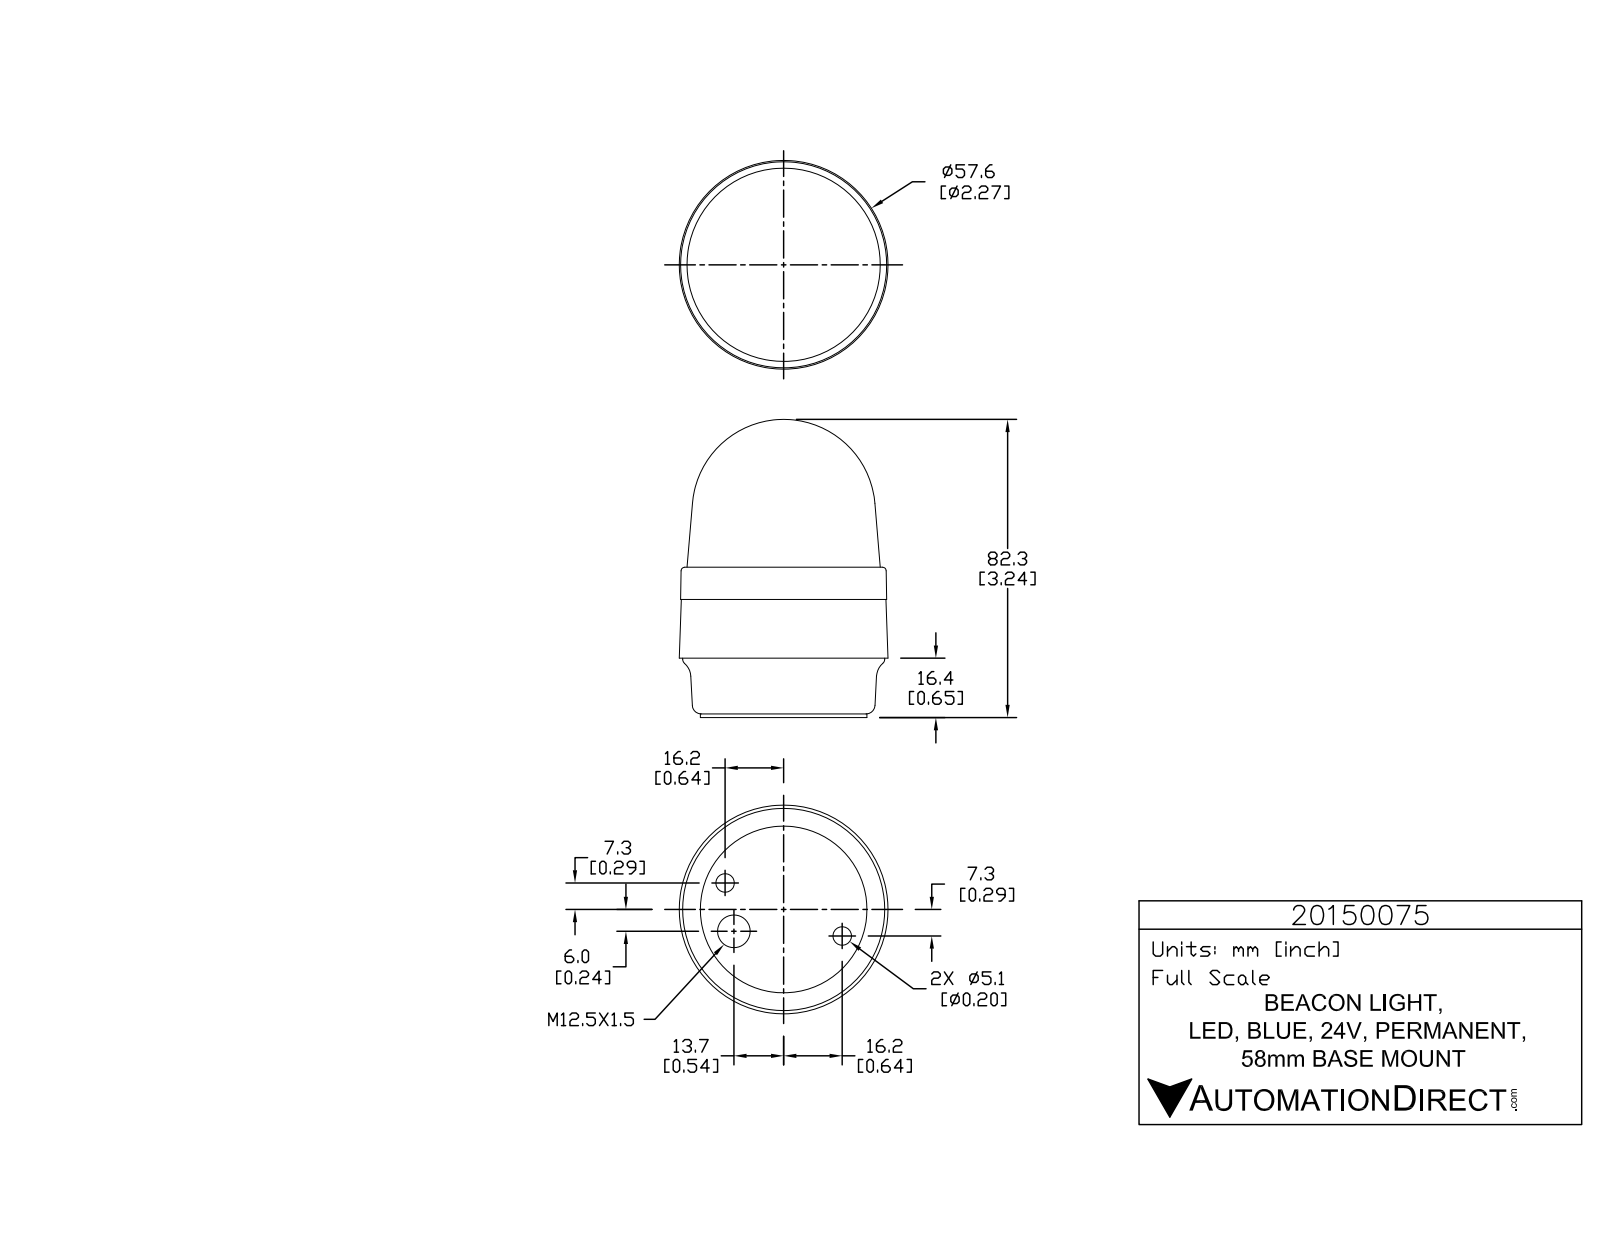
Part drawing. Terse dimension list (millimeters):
name: 20150075
written by: SolidWorks 2015 (AUTOMOTIVE_DESIGN)
unit: mm
bodies: 1 solid, 763 faces (527 planar, 145 cylindrical, 91 other)
size: 82.3 × 57.63 × 57.63
volume: 164 395 mm³; area: 16 261 mm²
holes: 3× ⌀0.99, 2× ⌀5.11, 1× ⌀9
bosses: 3× ⌀5.74, 3× ⌀1.43, 1× ⌀55.8, 1× ⌀46
rounds: 6× R0.2, 6× R0.21, 6× R0.21, 6× R3.32, 3× R0.1, 3× R0.12, 3× R0.19, 3× R0.2
face distances: 16.4, 1, 15.4, 41.5, 40.5, 25.1, 32.6, 31.6, 16.2, 8.9
hole spacings: 13.56, 29.94, 35.5
